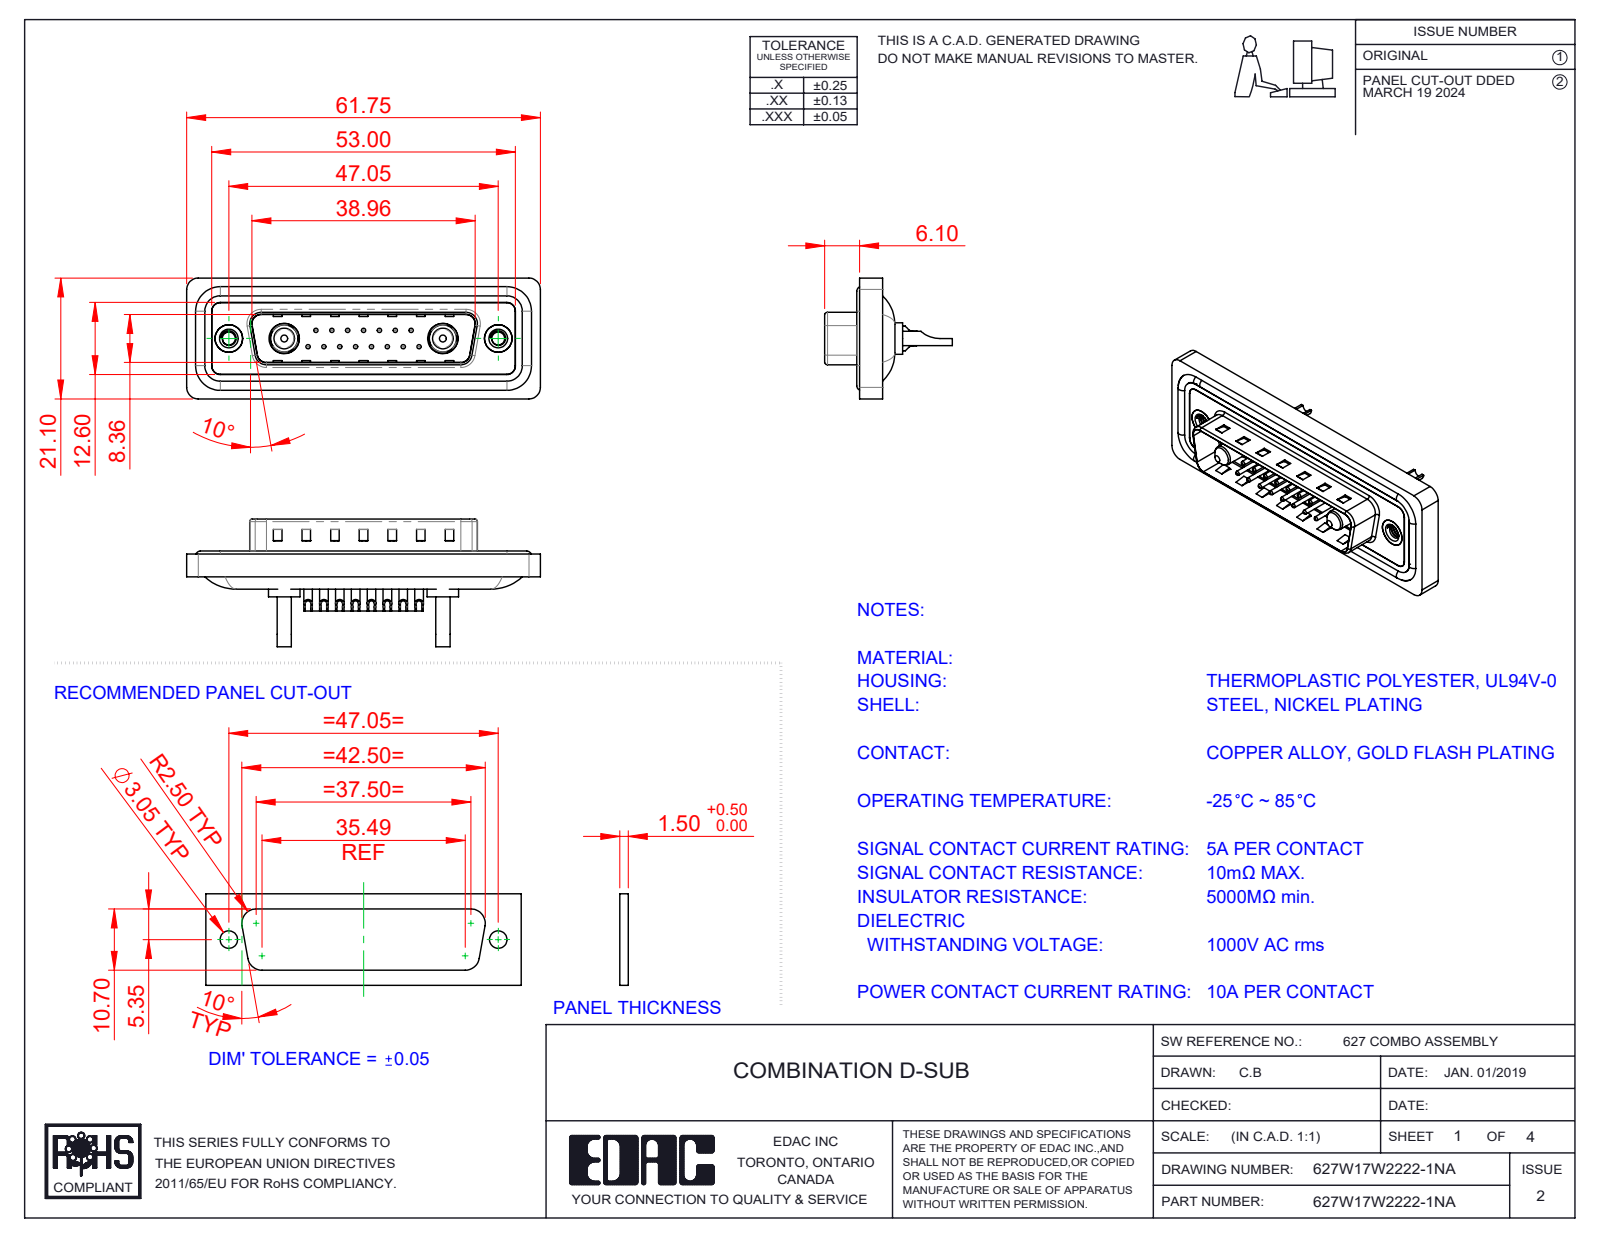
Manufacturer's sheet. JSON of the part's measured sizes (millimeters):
{"part_name": "627Combo Contact Row 2_22; 627Combo Housing_17W2; 627Combo Threaded Rivet_A; 627Combo Waterproof Housing_25 Contacts (+5 more)", "step_written_by": "SolidWorks 2023 (CONFIG_CONTROL_DESIGN)", "units": "millimeters", "bodies": {"solids": 26, "faces": 1126, "planar": 368, "cylindrical": 474, "other": 284}, "overall_size": [61.75, 22.3, 21.1], "volume_mm3": 7286, "surface_area_mm2": 12126, "round_holes": [[0.75, 15], [1, 15], [1.6, 15], [2, 15], [1.7, 2], [2.26, 2], [4, 2], [4.8, 2], [4.85, 2], [5, 2], [5.3, 2]], "round_bosses_or_shafts": [[1.5, 15], [1.6, 4], [5.5, 2], [5.2, 2], [4.9, 2], [4.75, 2], [3.75, 2], [3.6, 2]], "partial_cylinders_radius": [[1.5, 22], [2, 18], [0.5, 8], [1.6, 8], [1, 6], [0.25, 4], [0.6, 4], [0.65, 4]], "face_to_face_distances": [0.4, 1.5, 1.1, 1.6, 0.5, 3.1, 2.9, 0.82, 9.58, 4.1], "hole_center_spacings": [3.16, 2.77, 5.54, 8.31, 5.04, 7.49, 11.08, 5.03]}
